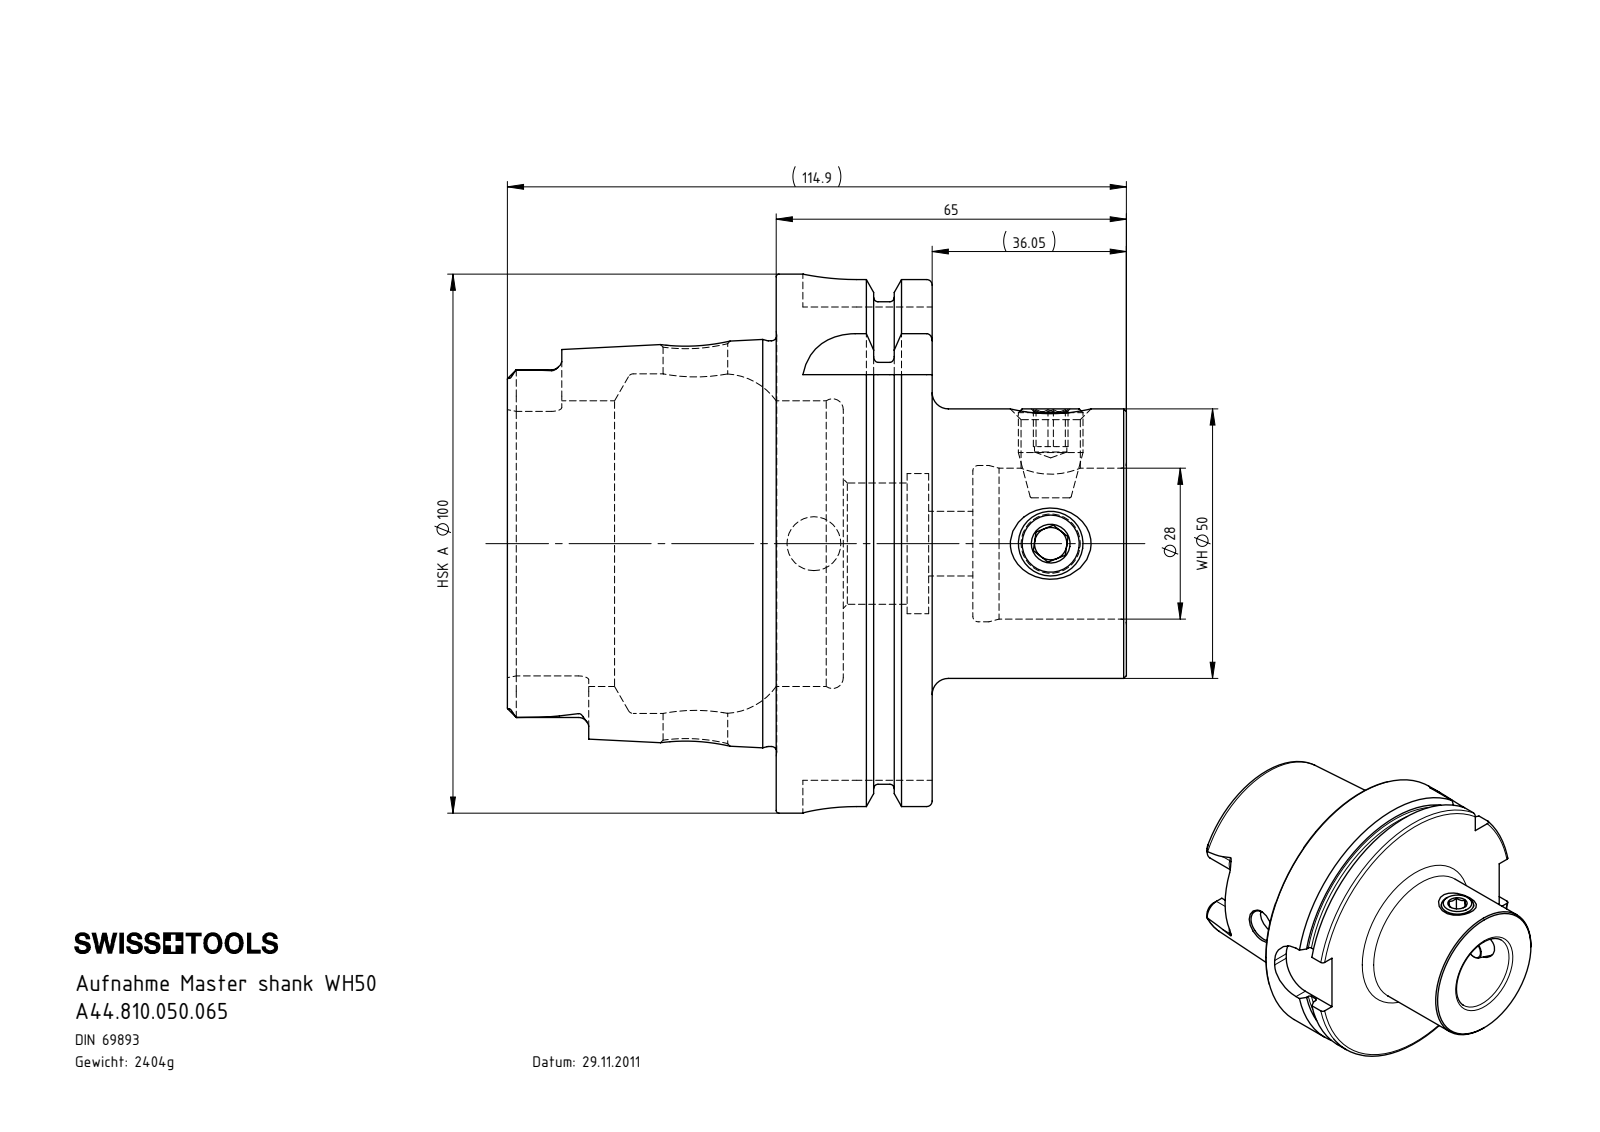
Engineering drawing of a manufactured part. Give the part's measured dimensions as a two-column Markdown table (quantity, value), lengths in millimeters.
| quantity | value |
| --- | --- |
| part name | HA0-WH5.K01.065_A_Weichbearbeitung; HA0-WH5.K01.065; WH5-ER1.001.017 |
| STEP written by | SolidWorks 2015 (AUTOMOTIVE_DESIGN) |
| units | millimeters |
| bodies | 3 solids, 230 faces (71 planar, 64 cylindrical, 95 other) |
| overall size | 114.8 × 100.3 × 100.3 |
| volume | 309 650 mm³ |
| surface area | 60 012 mm² |
| round holes (diameter × count) | 6 × 2, 11 × 2, 12 × 2, 10 × 1, 22.5 × 1, 26 × 1, 28 × 1, 29 × 1, 52.7 × 1, 63 × 1 |
| round bosses / shafts (diameter × count) | 12 × 2, 100.3 × 1, 91.95 × 1, 75.26 × 1, 50 × 1 |
| partial cylindrical surfaces (radius × count) | 1.9 × 8, 4.88 × 4, 10 × 4 |
| main face-to-face distances | 28.95, 16.5, 12.45, 65, 52.55, 36.05, 49.8, 62.25, 78.75, 114.8 |
| hole center spacings | 43.85, 65.85 |
